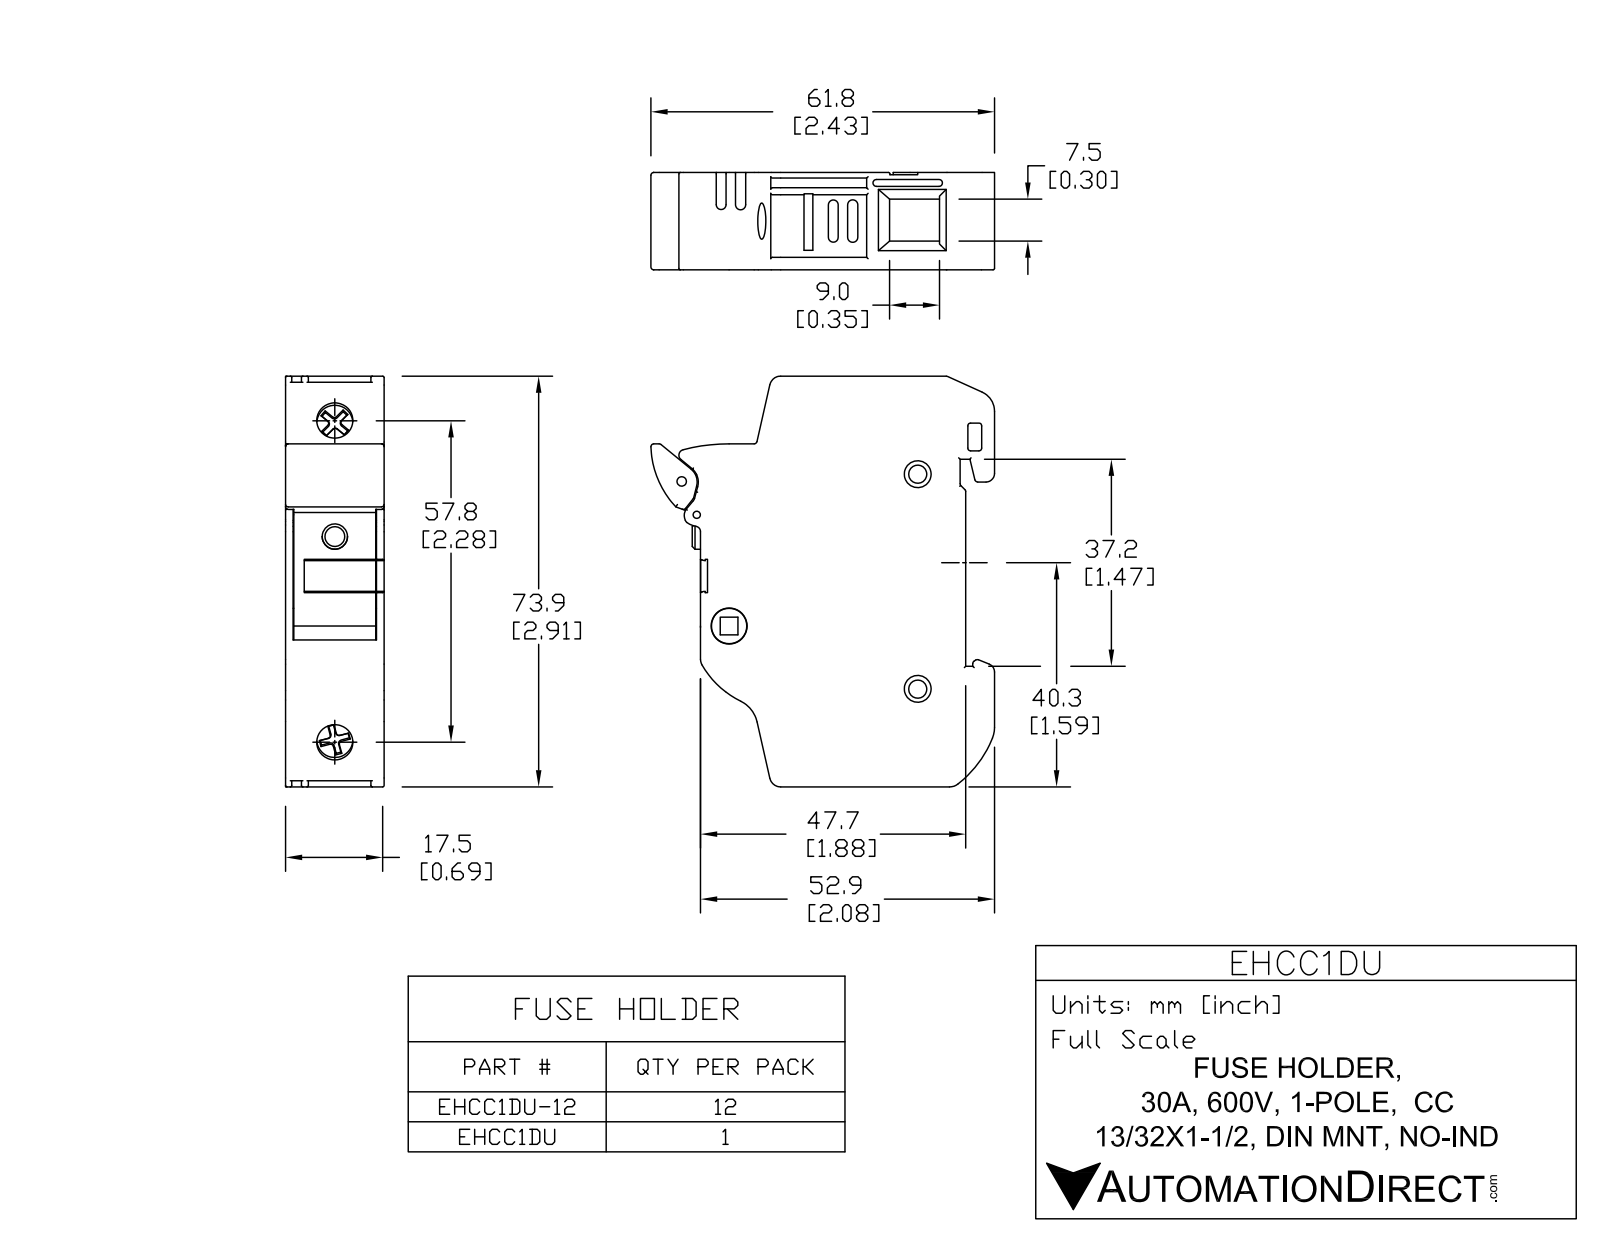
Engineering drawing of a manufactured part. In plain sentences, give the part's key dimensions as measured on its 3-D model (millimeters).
The part is named "EHCC1DU". Its 3-D file was written by "SolidWorks 2011 (AUTOMOTIVE_DESIGN)". It is 1 solid with 626 faces: 245 planar, 214 cylindrical and 167 other. Overall it measures 73.88 by 61.82 by 17.5 millimeters. Its volume is 52 717 cubic millimeters and its surface area 19 521 square millimeters. Round holes: 2 of diameter 3.25, 2 of diameter 4.83, 2 of diameter 6.5, 1 of diameter 1.3, 1 of diameter 1.7, 1 of diameter 6.48. Round bosses or shafts: 1 of diameter 6.35. Partial cylindrical surfaces (rounded edges, fillets, slot ends): 73 of radius 0.25, 21 of radius 0.5, 10 of radius 2, 9 of radius 0.51, 7 of radius 1, 4 of radius 0.62, 3 of radius 0.89, 3 of radius 0.92. The main face-to-face distances are 17.5, 1.25, 1.58, 16.25, 1.37, 16.13, 14.88, 27.51, 29.09, 22.94. The hole center spacings are 6.58, 20.83, 27.36, 35.77, 35.79, 38.61, 38.66, 40.43.
